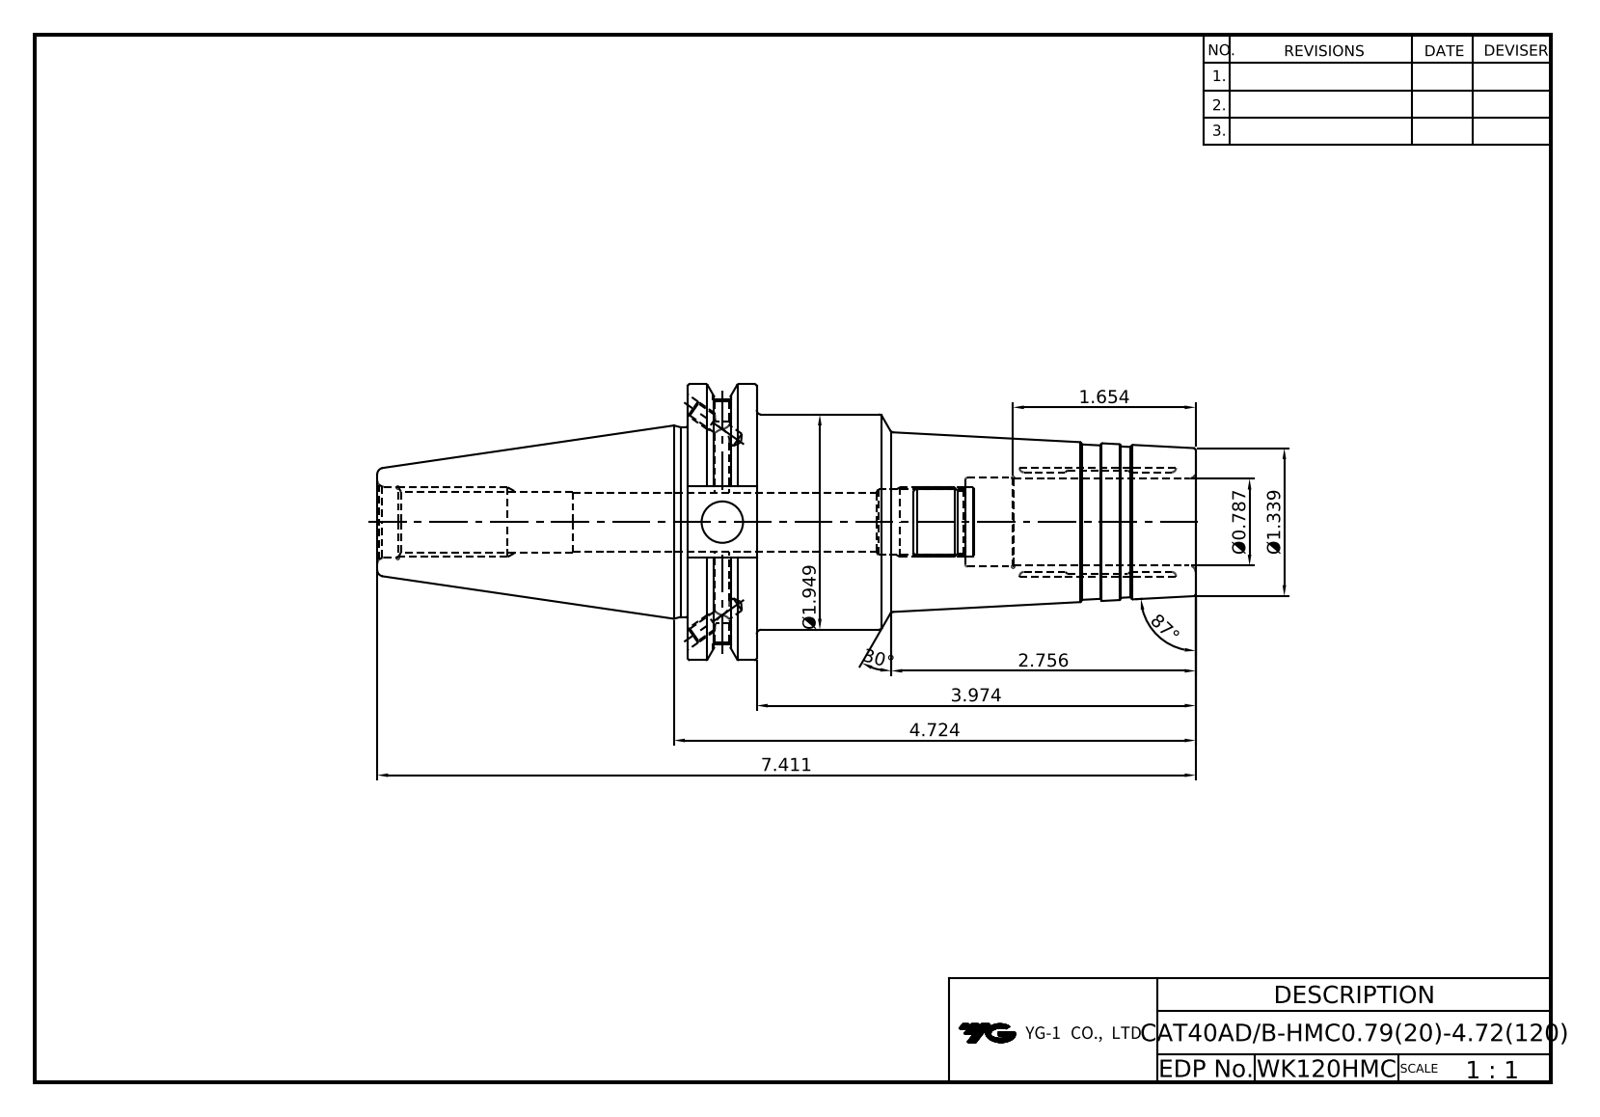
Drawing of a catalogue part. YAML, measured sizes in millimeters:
part_name: "LO-CAT40ADB-HMC20-120"
step_written_by: "Autodesk Inventor 2020 (AUTOMOTIVE_DESIGN)"
units: millimeters
bodies: {solids: 1, faces: 106, planar: 36, cylindrical: 30, other: 40}
overall_size: [188.25, 63.5, 61.09]
volume: 213388
surface_area: 38506
round_holes:
  - {diameter: 3.24, count: 4}
  - {diameter: 4, count: 2}
  - {diameter: 4.2, count: 2}
  - {diameter: 9.53, count: 1}
  - {diameter: 13, count: 1}
  - {diameter: 13.39, count: 1}
  - {diameter: 14.92, count: 1}
  - {diameter: 16.3, count: 1}
  - {diameter: 20, count: 1}
  - {diameter: 20.4, count: 1}
round_bosses_or_shafts:
  - {diameter: 63.5, count: 1}
  - {diameter: 49.5, count: 1}
  - {diameter: 43.6, count: 1}
partial_cylinders:
  - {radius: 8.19, count: 1}
  - {radius: 28.15, count: 1}
face_to_face_distances: [15.88, 116.83, 100.95, 47.6, 16.38, 63.83, 47.95, 53, 71.42, 87.3]
